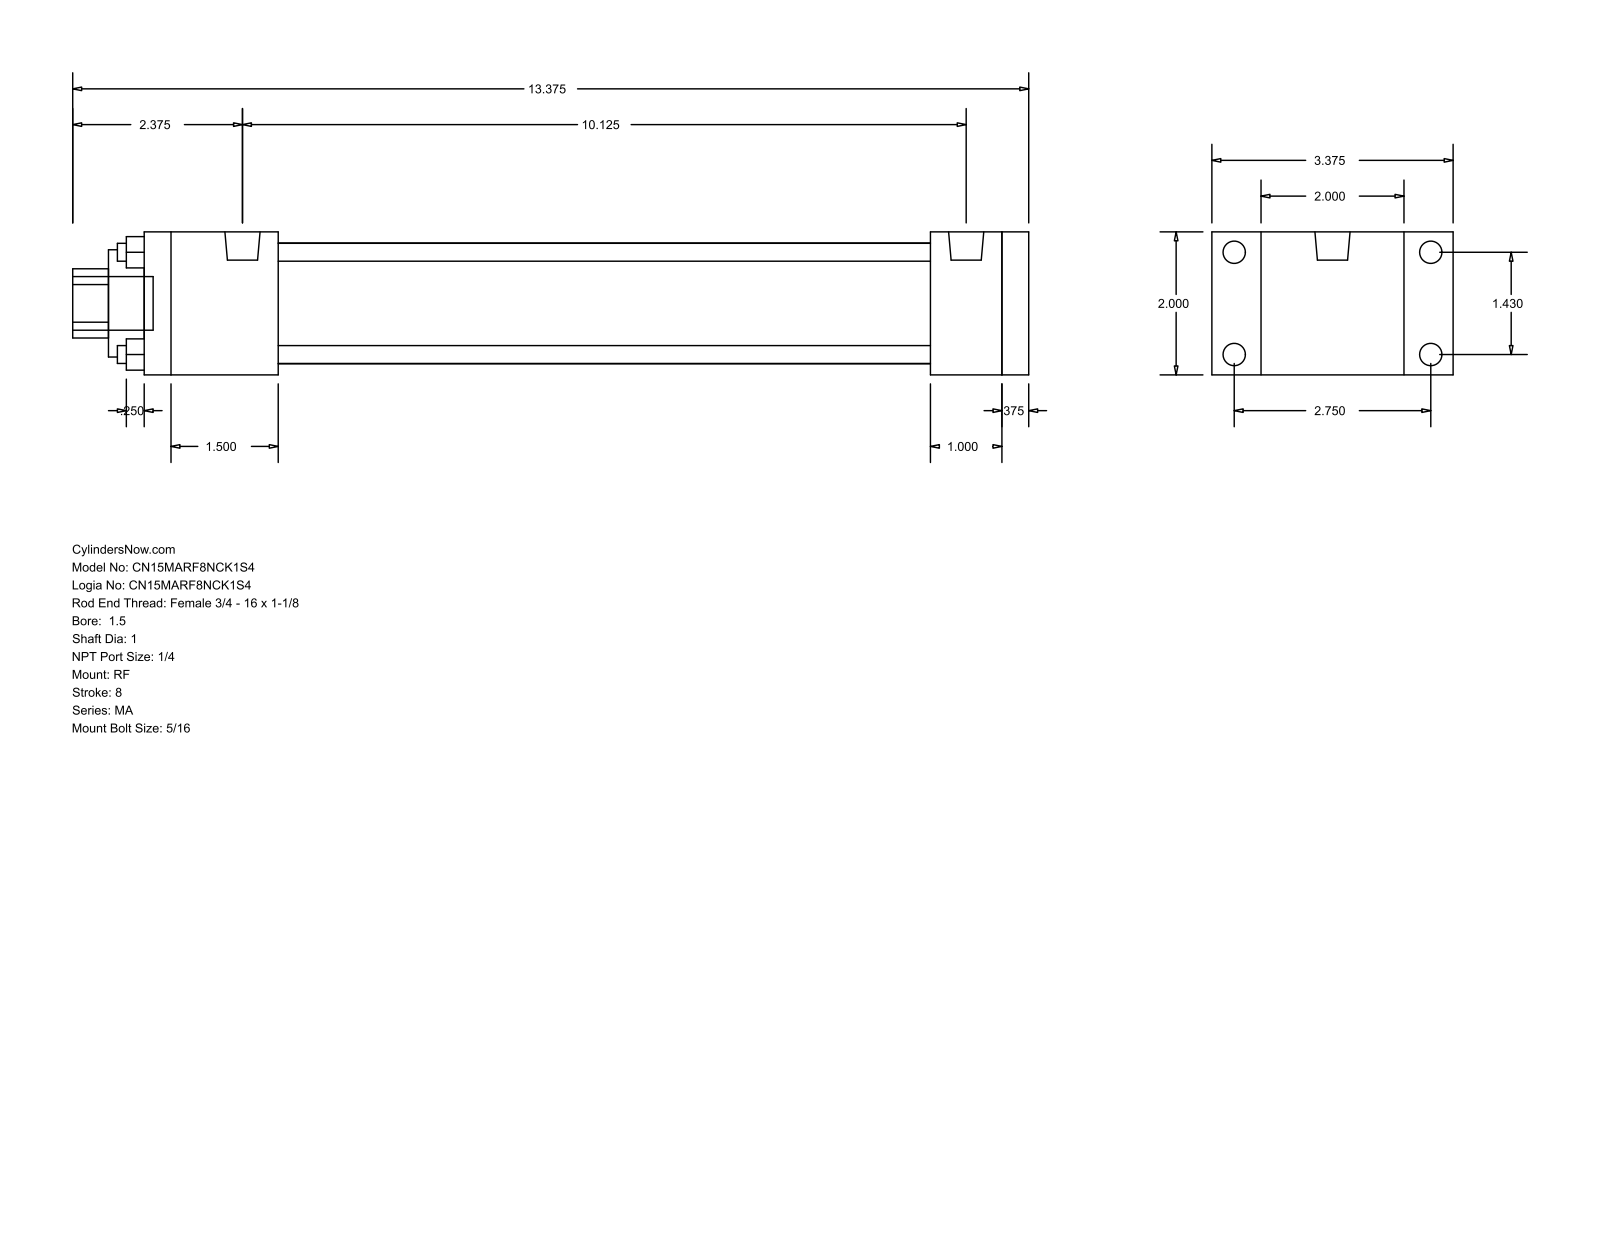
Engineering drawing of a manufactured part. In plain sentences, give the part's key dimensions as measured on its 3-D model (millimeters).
The part is named "MA_RF__0150_1". Its 3-D file was written by "GSSL Pune (CONFIG_CONTROL_DESIGN)". It is 0 solids with 92 faces: 64 planar, 28 cylindrical and 0 other. Overall it measures 339.73 by 85.72 by 50.8 millimeters. Round holes: 4 of diameter 6.35, 1 of diameter 25.4, 1 of diameter 38.1, 1 of diameter 42.93. Round bosses or shafts: 8 of diameter 7.94, 2 of diameter 12.49, 1 of diameter 19.05. Partial cylindrical surfaces (rounded edges, fillets, slot ends): 1 of radius 12.29. The main face-to-face distances are 50.8, 9.53, 304.8, 25.4, 314.33, 279.4, 34.93, 47.63, 231.77, 257.17. The hole center spacings are 25.68, 36.32, 51.36.
